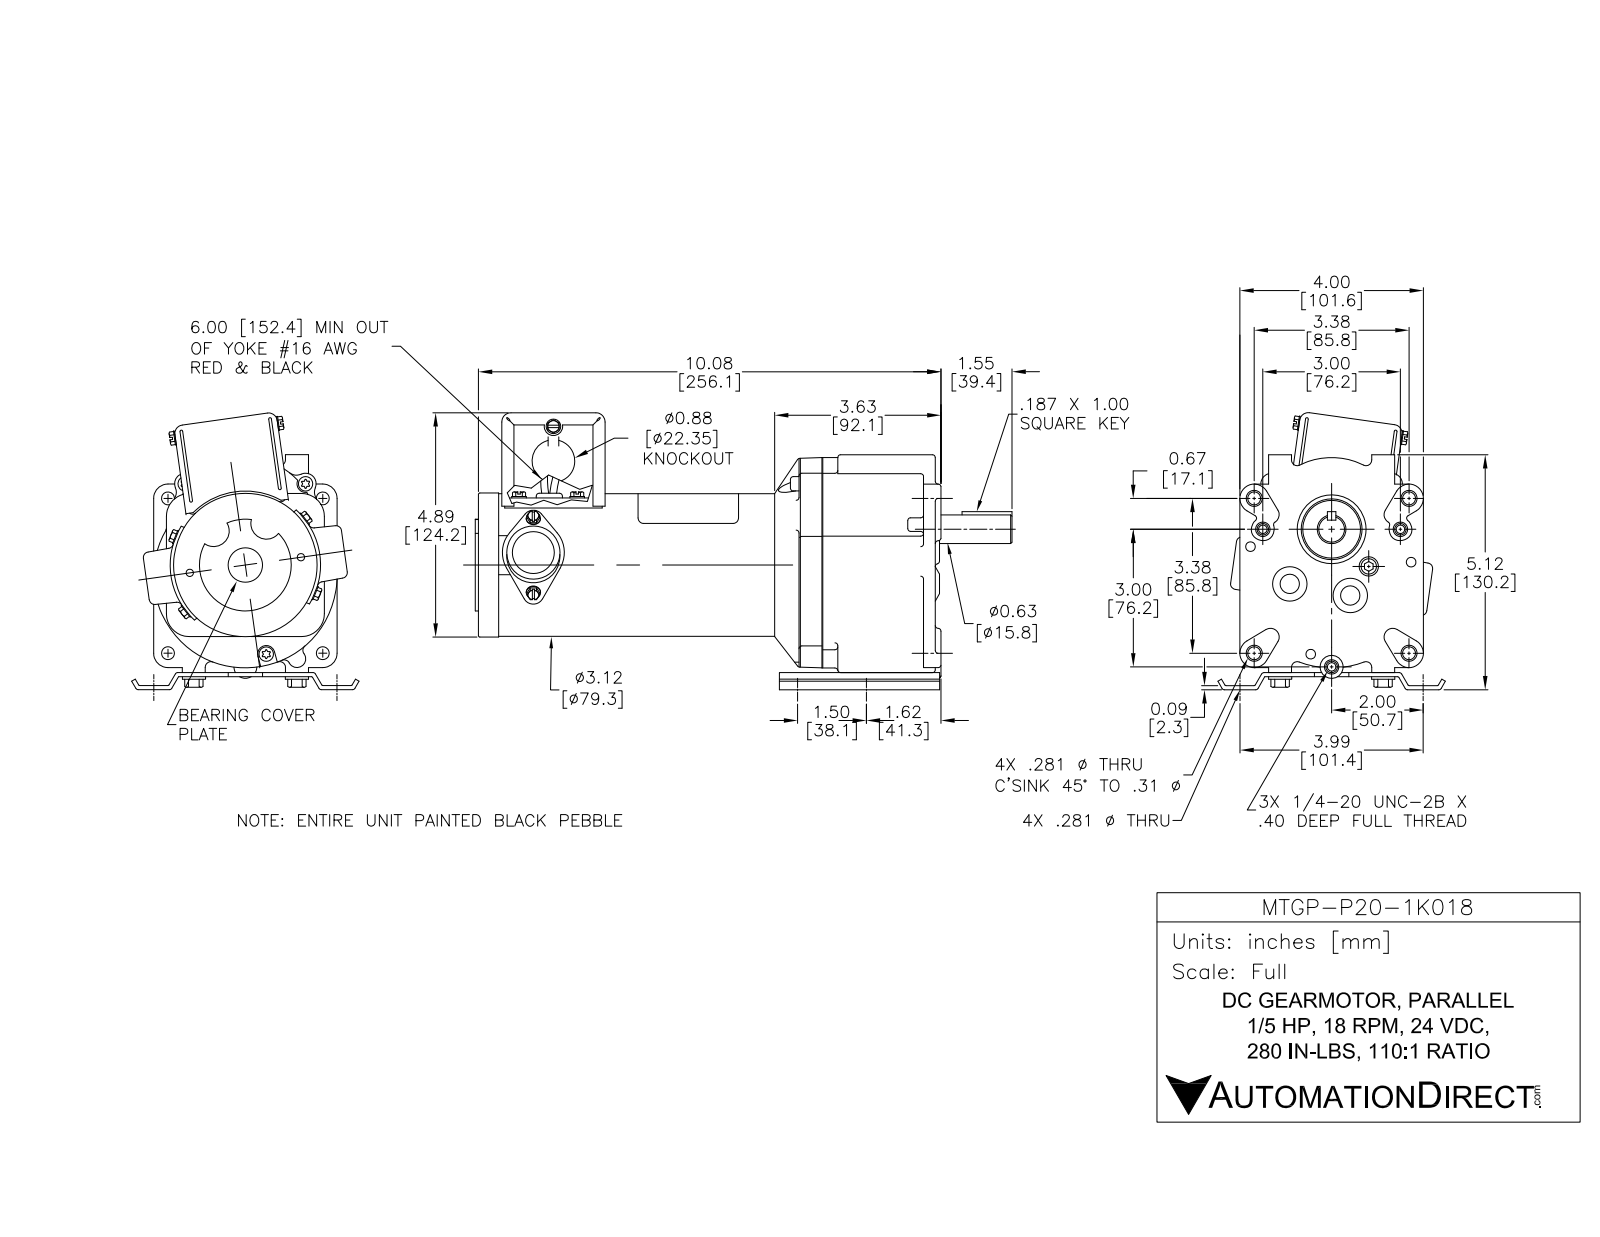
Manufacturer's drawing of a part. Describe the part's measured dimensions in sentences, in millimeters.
The part is named "MTGP-P20-1K018". Its 3-D file was written by "SolidWorks 2014 (AUTOMOTIVE_DESIGN)". It is 53 solids with 984 faces: 567 planar, 365 cylindrical and 52 other. Overall it measures 297.1 by 157.7 by 125.5 millimeters. Its volume is 1 067 000 cubic millimeters and its surface area 303 600 square millimeters. Round holes: 11 of diameter 7.6, 5 of diameter 12.7, 4 of diameter 6.4, 4 of diameter 8.8, 3 of diameter 5.3, 2 of diameter 3.2, 2 of diameter 5, 2 of diameter 5.3, 2 of diameter 8.8, 1 of diameter 9.5, 1 of diameter 11.7, 1 of diameter 15.9. Round bosses or shafts: 5 of diameter 8, 4 of diameter 7.6, 3 of diameter 5.3, 2 of diameter 11.7, 2 of diameter 2.5, 1 of diameter 80.2, 1 of diameter 33.7, 1 of diameter 15.9. Partial cylindrical surfaces (rounded edges, fillets, slot ends): 28 of radius 0.5, 23 of radius 2.5, 8 of radius 0.6, 7 of radius 6.4, 4 of radius 4, 4 of radius 4.8, 4 of radius 4.9, 4 of radius 5.9. The main face-to-face distances are 34.9, 88.8, 53.8, 2.3, 0.8, 6.4, 1.6, 1.3, 36.2, 90. The hole center spacings are 41.1, 31.2, 38.1, 38.2, 40.7, 75.5, 85.7, 175.5.
